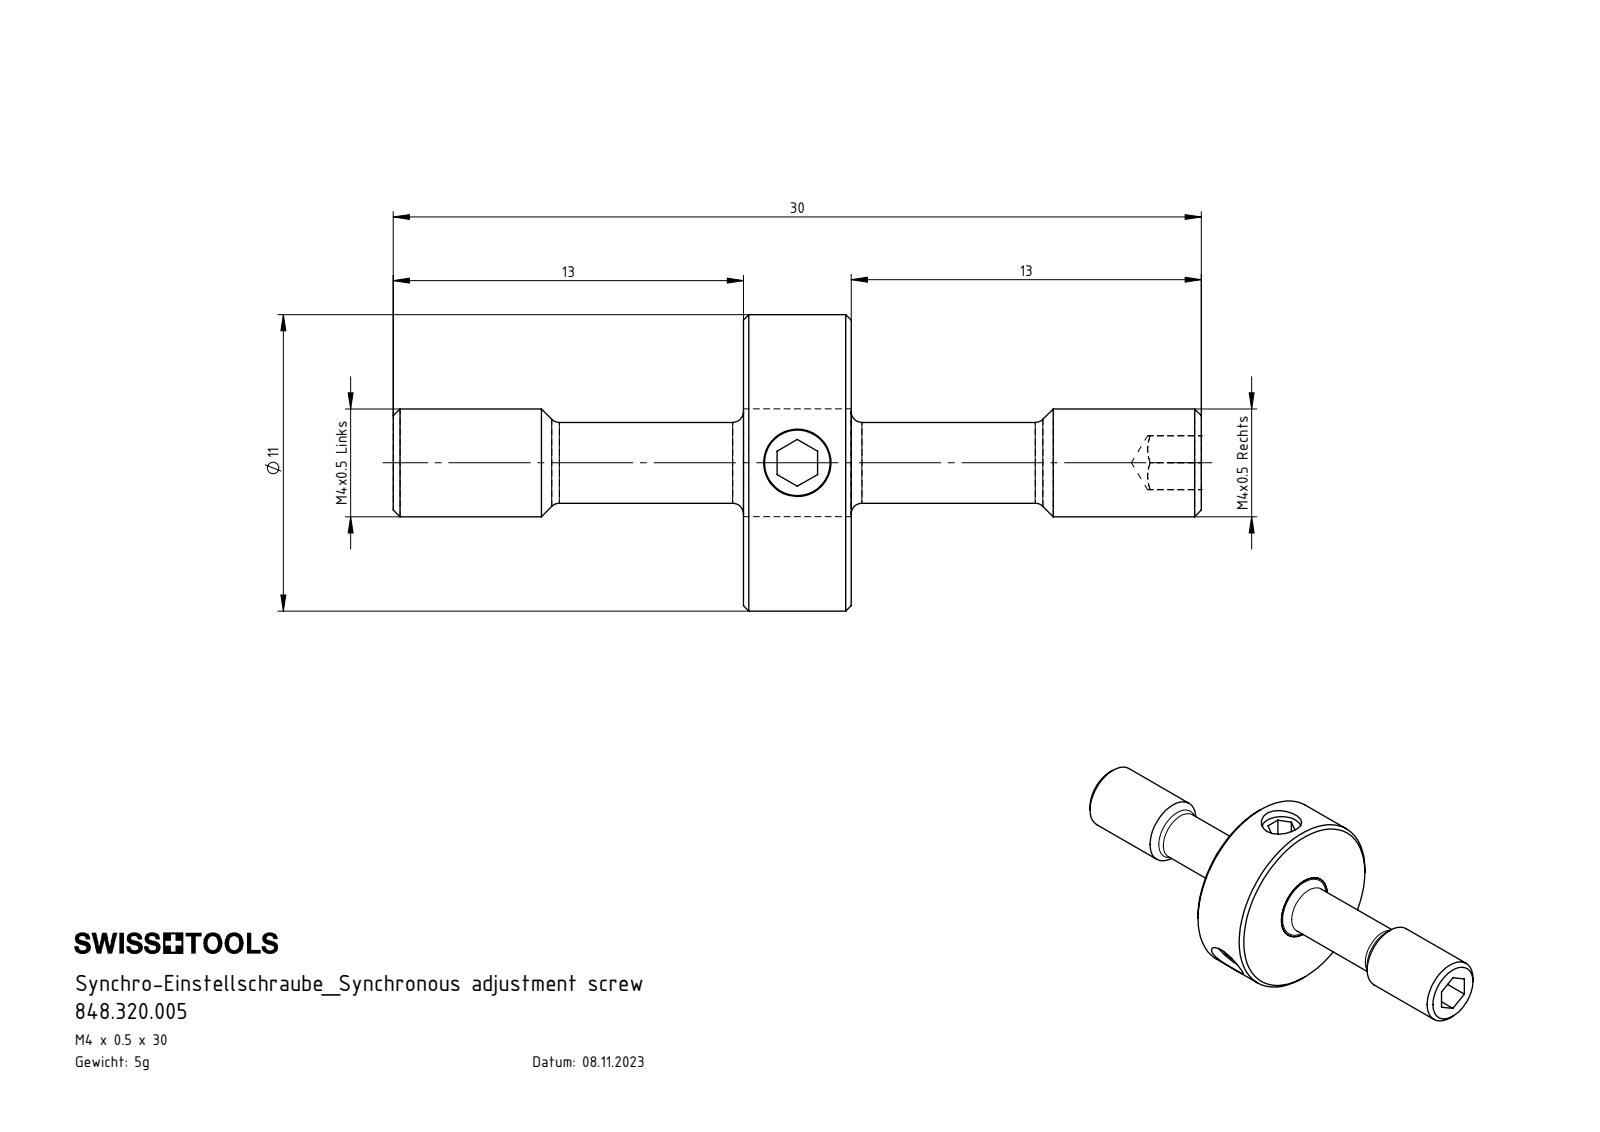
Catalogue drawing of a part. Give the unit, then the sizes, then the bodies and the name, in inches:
Units: inches
Overall size (bounding box): 1.181 × 0.433 × 0.433
Round holes (diameter × count): ⌀0.098 ×3
Round bosses / shafts (diameter × count): ⌀0.118 ×4, ⌀0.433 ×1, ⌀0.157 ×1
Main face-to-face distances: 0.157, 0.512, 0.669, 0.059, 0.079, 0.561, 0.62, 0.049, 0.108, 0.118
Volume: 0.037 in³ · Surface area: 1.43 in²
Bodies: 5 solids, 99 faces (39 planar, 26 cylindrical, 34 other)
Part name (STEP PRODUCT): Z25-ER3.002.004_A; 848.320.005; Z32-ER3.001.030_A; ISO 4026 - M3 x 3
STEP written by: SolidWorks 2022 (AUTOMOTIVE_DESIGN)
